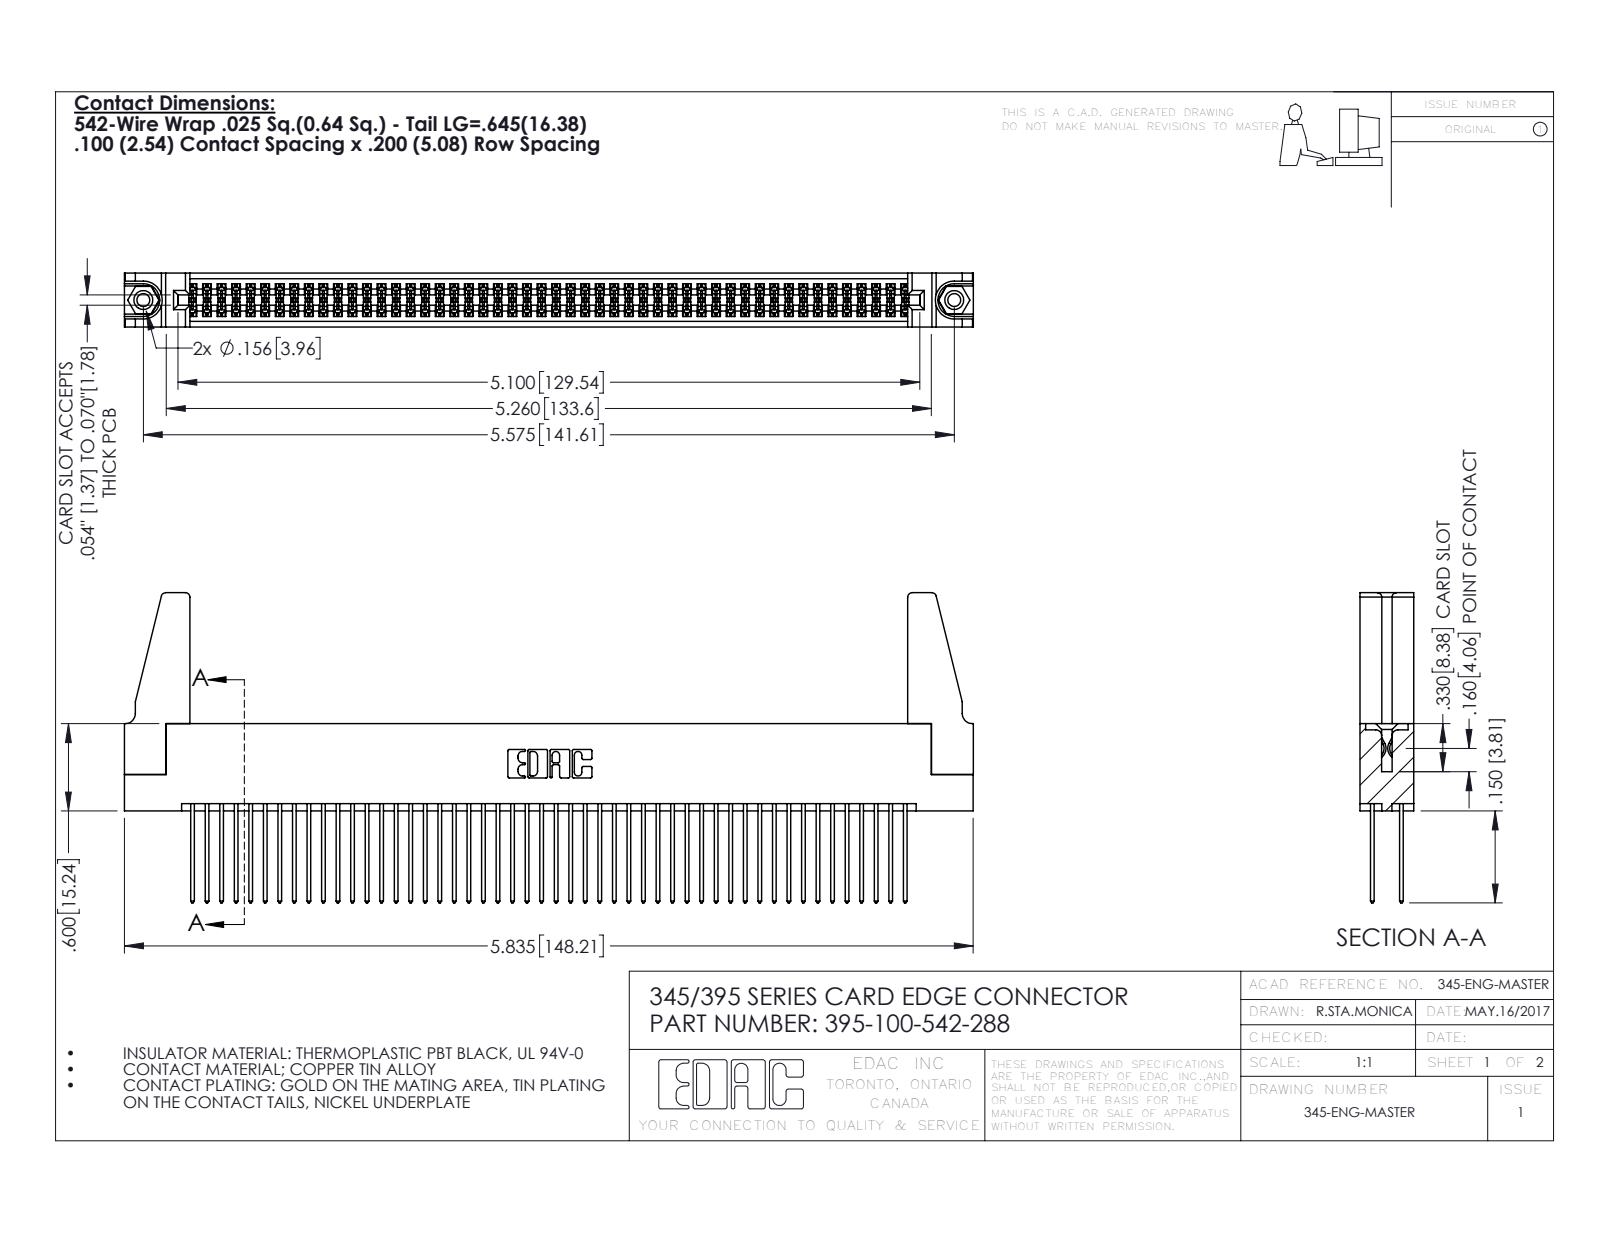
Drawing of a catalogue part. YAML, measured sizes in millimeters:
part_name: "345-250-001_345-250-001-102; 395-100-542-288; 345-292-001_345-293-142; 345-220-078_345-220-088 (+1 more)"
step_written_by: "SolidWorks 2016 (CONFIG_CONTROL_DESIGN)"
units: millimeters
bodies: {solids: 105, faces: 5250, planar: 3452, cylindrical: 1782, other: 16}
overall_size: [148.2, 54.2, 9.4]
volume: 18190
surface_area: 27540
round_holes:
  - {diameter: 2.3, count: 2}
  - {diameter: 3.2, count: 2}
  - {diameter: 4, count: 2}
  - {diameter: 1.6, count: 1}
round_bosses_or_shafts:
  - {diameter: 3.9, count: 2}
partial_cylinders:
  - {radius: 0.2, count: 150}
  - {radius: 0.3, count: 100}
  - {radius: 0.3, count: 22}
  - {radius: 0.8, count: 8}
  - {radius: 0.2, count: 6}
  - {radius: 0.8, count: 6}
  - {radius: 0.7, count: 3}
  - {radius: 0.4, count: 2}
face_to_face_distances: [1.8, 7.6, 5.1, 2.5, 6.9, 0.6, 9.4, 5.7, 4.4, 3.8]
hole_center_spacings: [6.9, 135.6, 141.6]
